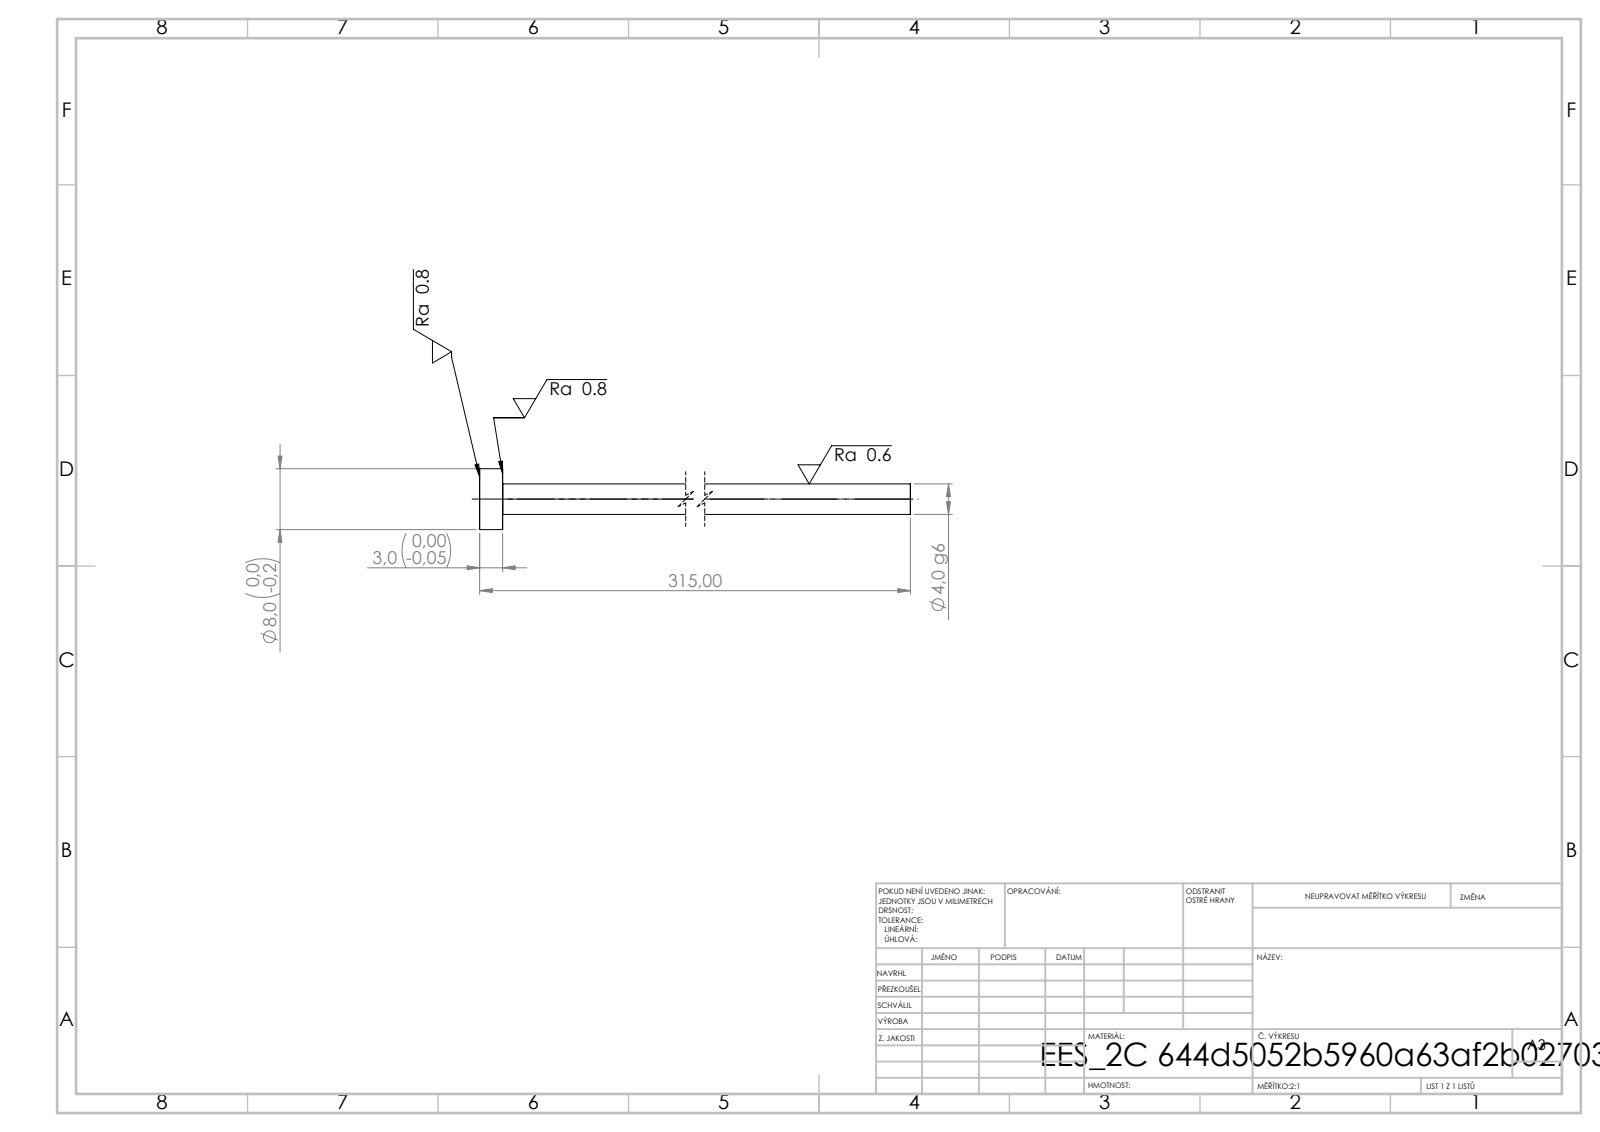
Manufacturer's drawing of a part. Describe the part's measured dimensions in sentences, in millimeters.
Its 3-D file was written by "SolidWorks 2019 (CONFIG_CONTROL_DESIGN)". It is 1 solid with 7 faces: 3 planar, 4 cylindrical and 0 other. Overall it measures 315 by 8 by 8 millimeters. Its volume is 4 072 cubic millimeters and its surface area 4 097 square millimeters. Round bosses or shafts: 1 of diameter 8, 1 of diameter 4. The main face-to-face distances are 3, 315, 312.
